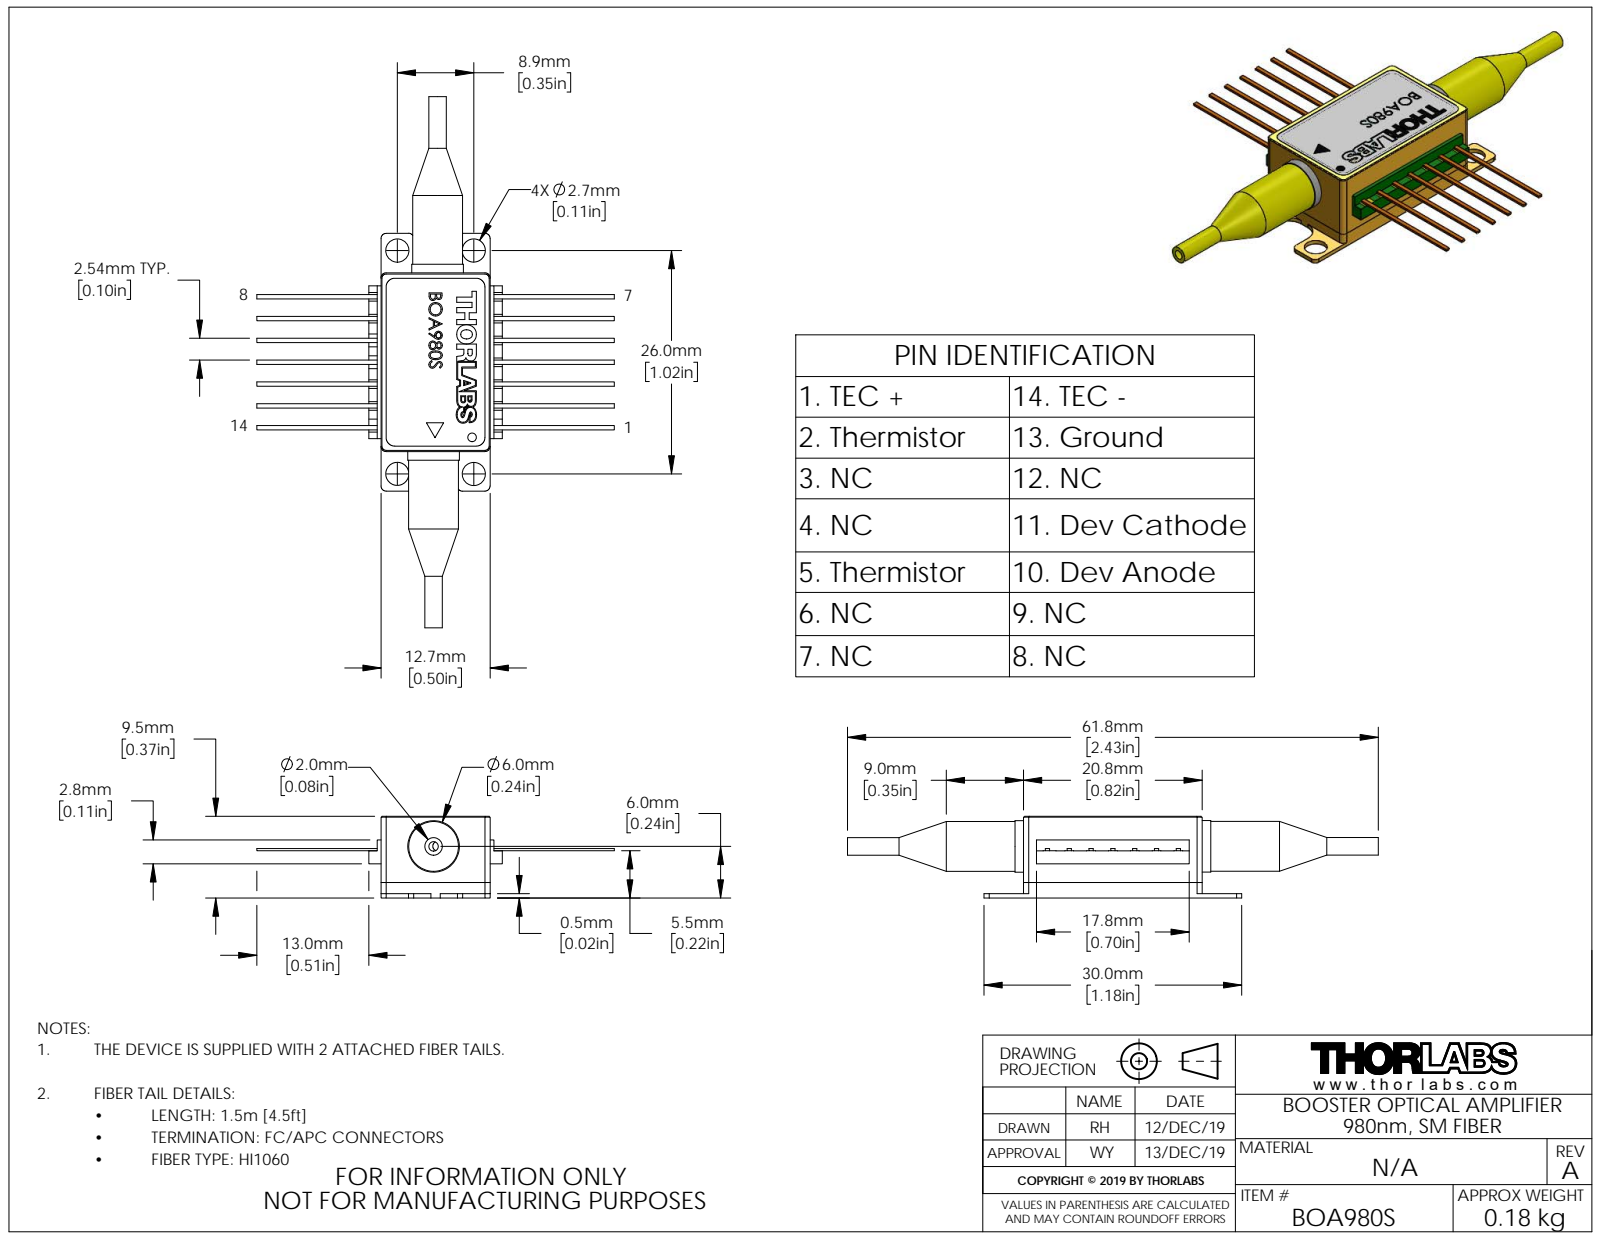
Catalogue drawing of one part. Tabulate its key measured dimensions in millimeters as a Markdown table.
| quantity | value |
| --- | --- |
| part name | QTN039463-E0W |
| STEP written by | SolidWorks 2018 (AUTOMOTIVE_DESIGN) |
| units | millimeters |
| bodies | 0 solids, 356 faces (246 planar, 52 cylindrical, 58 other) |
| overall size | 61.8 × 41.6 × 9.5 |
| round holes (diameter × count) | 2.7 × 4, 1.1 × 2, 1 × 1 |
| round bosses / shafts (diameter × count) | 6 × 2, 5.8 × 2, 2.04 × 2 |
| partial cylindrical surfaces (radius × count) | 0.6 × 12, 0.5 × 4, 2 × 4, 1 × 2 |
| main face-to-face distances | 9.49, 12.7, 3.97, 5.52, 5.5, 1.53, 3.99, 0.5, 5.75, 1.78 |
| hole center spacings | 8.9, 26, 27.48, 0.46, 4.26, 9.69, 21.74, 23.42 |
